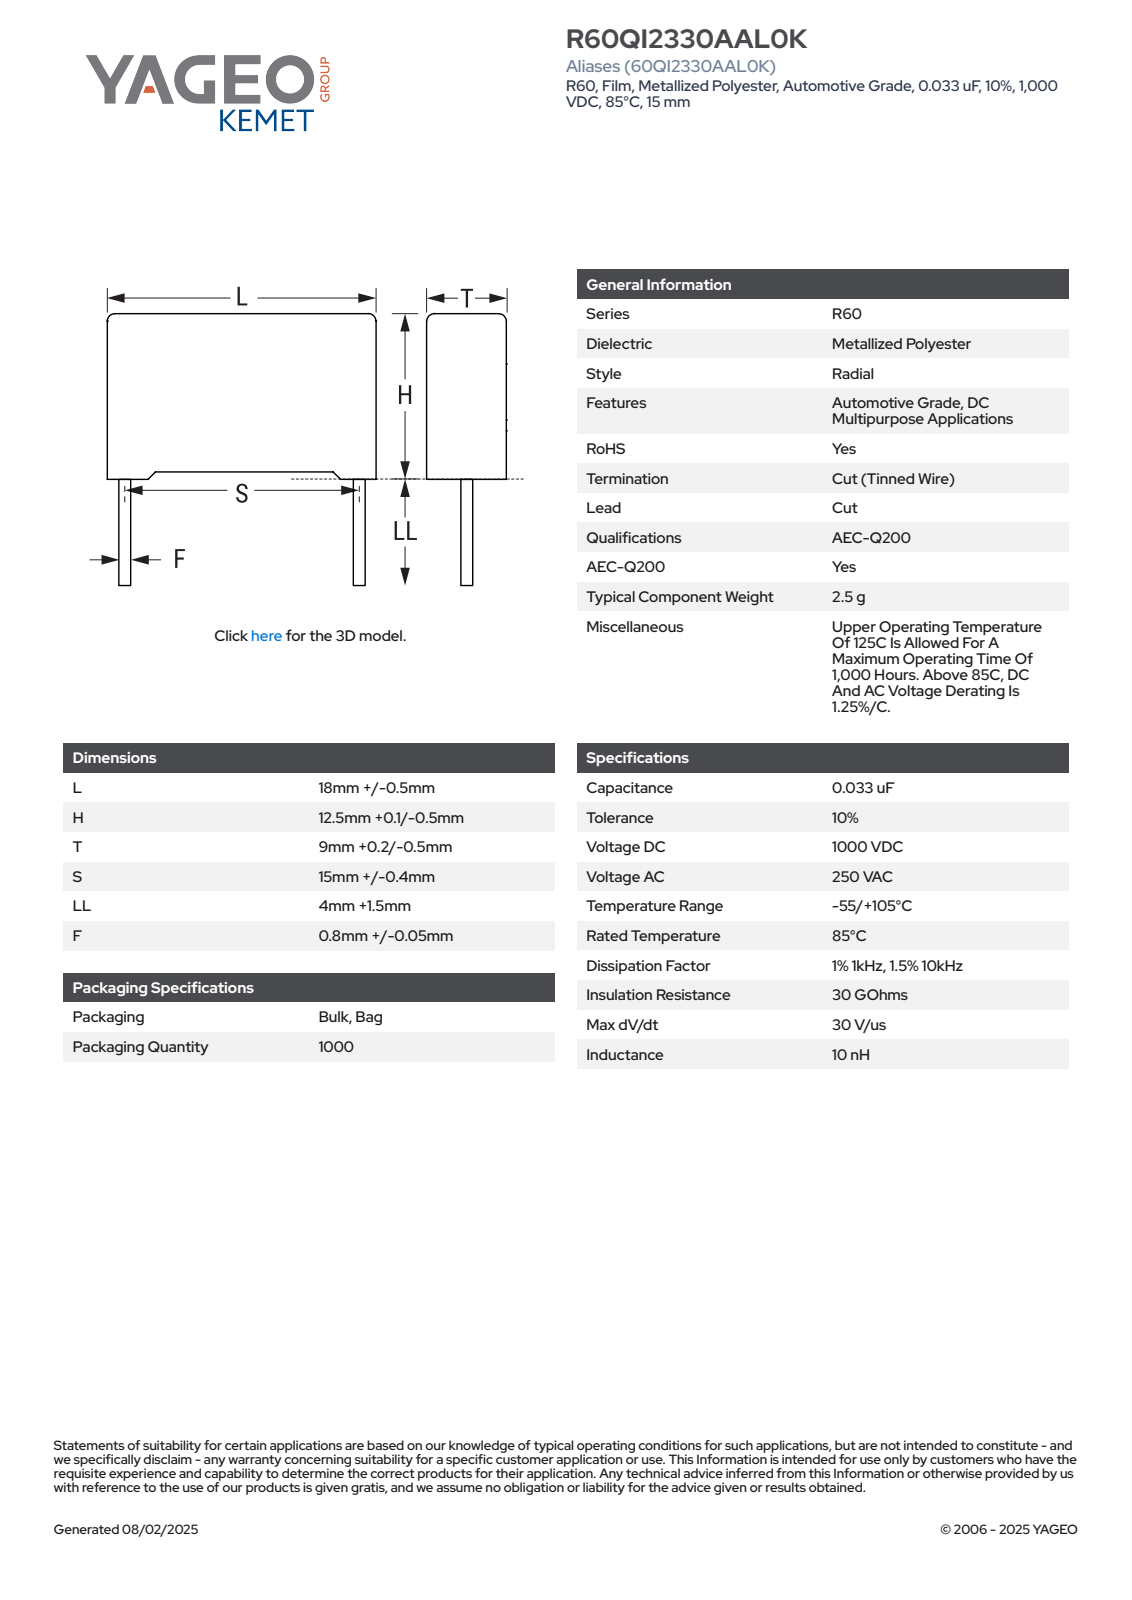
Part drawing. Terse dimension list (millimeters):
name: CFR_RB2_18X12.5X9_L18.5H12.6T9.2S15LL5.5F0.85
written by: SolidWorks 2021 (AUTOMOTIVE_DESIGN)
unit: mm
bodies: 4 solids, 85 faces (77 planar, 8 cylindrical, 0 other)
size: 18.5 × 18.1 × 9.21
volume: 2 039 mm³; area: 1 104 mm²
bosses: 2× ⌀0.85
rounds: 4× R0.5
face distances: 9.2, 11.85, 18.5, 0.62, 0.75, 12.6, 8.58, 0.43, 0.32, 12.17
